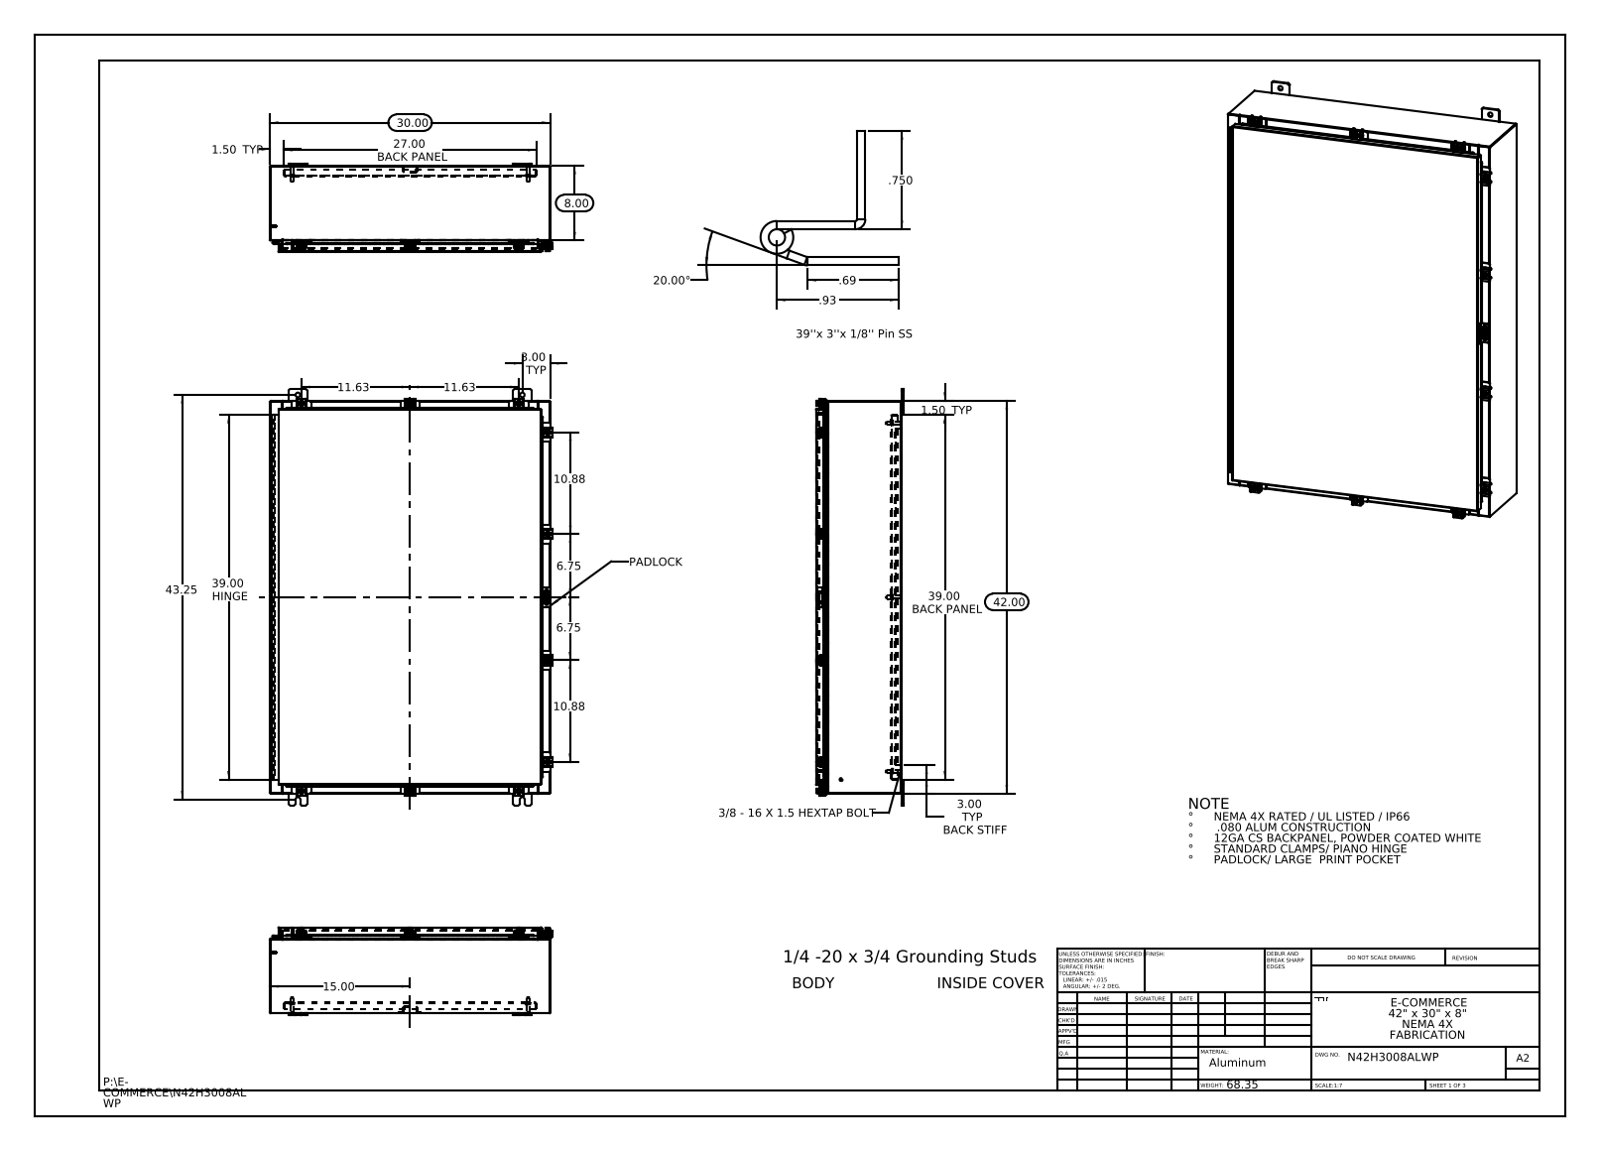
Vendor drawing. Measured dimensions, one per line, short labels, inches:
name: N42H3008ALWP Mounting Studs; N42H3008ALWP Backpanel; N42H3008ALWP 22104005_DEFAULT; N42H3008ALWP Top (+8 more)
written by: SolidWorks 2013 (CONFIG_CONTROL_DESIGN)
unit: in
bodies: 72 solids, 2743 faces (1426 planar, 1157 cylindrical, 160 other)
size: 44.5 × 30.211 × 9.389
volume: 439.2 in³; area: 10 916 in²
holes: 10× ⌀0.213, 10× ⌀0.26, 10× ⌀0.5, 2× ⌀0.125, 1× ⌀0.125
bosses: 11× ⌀0.25, 10× ⌀0.5, 10× ⌀0.399, 6× ⌀0.625, 6× ⌀0.375, 6× ⌀0.33, 2× ⌀0.315, 2× ⌀0.236
rounds: 46× R0.06, 31× R0.013, 25× R0.088, 24× R0.19, 20× R0.12, 20× R0.141, 15× R0.05, 14× R0.08
face distances: 0.075, 9.126, 9.051, 0.104, 9.201, 1, 8.126, 1.075, 8.051, 1.179
hole spacings: 2.326, 18.625, 20.75, 24.268, 31.376, 39.363, 41.326, 43.05
